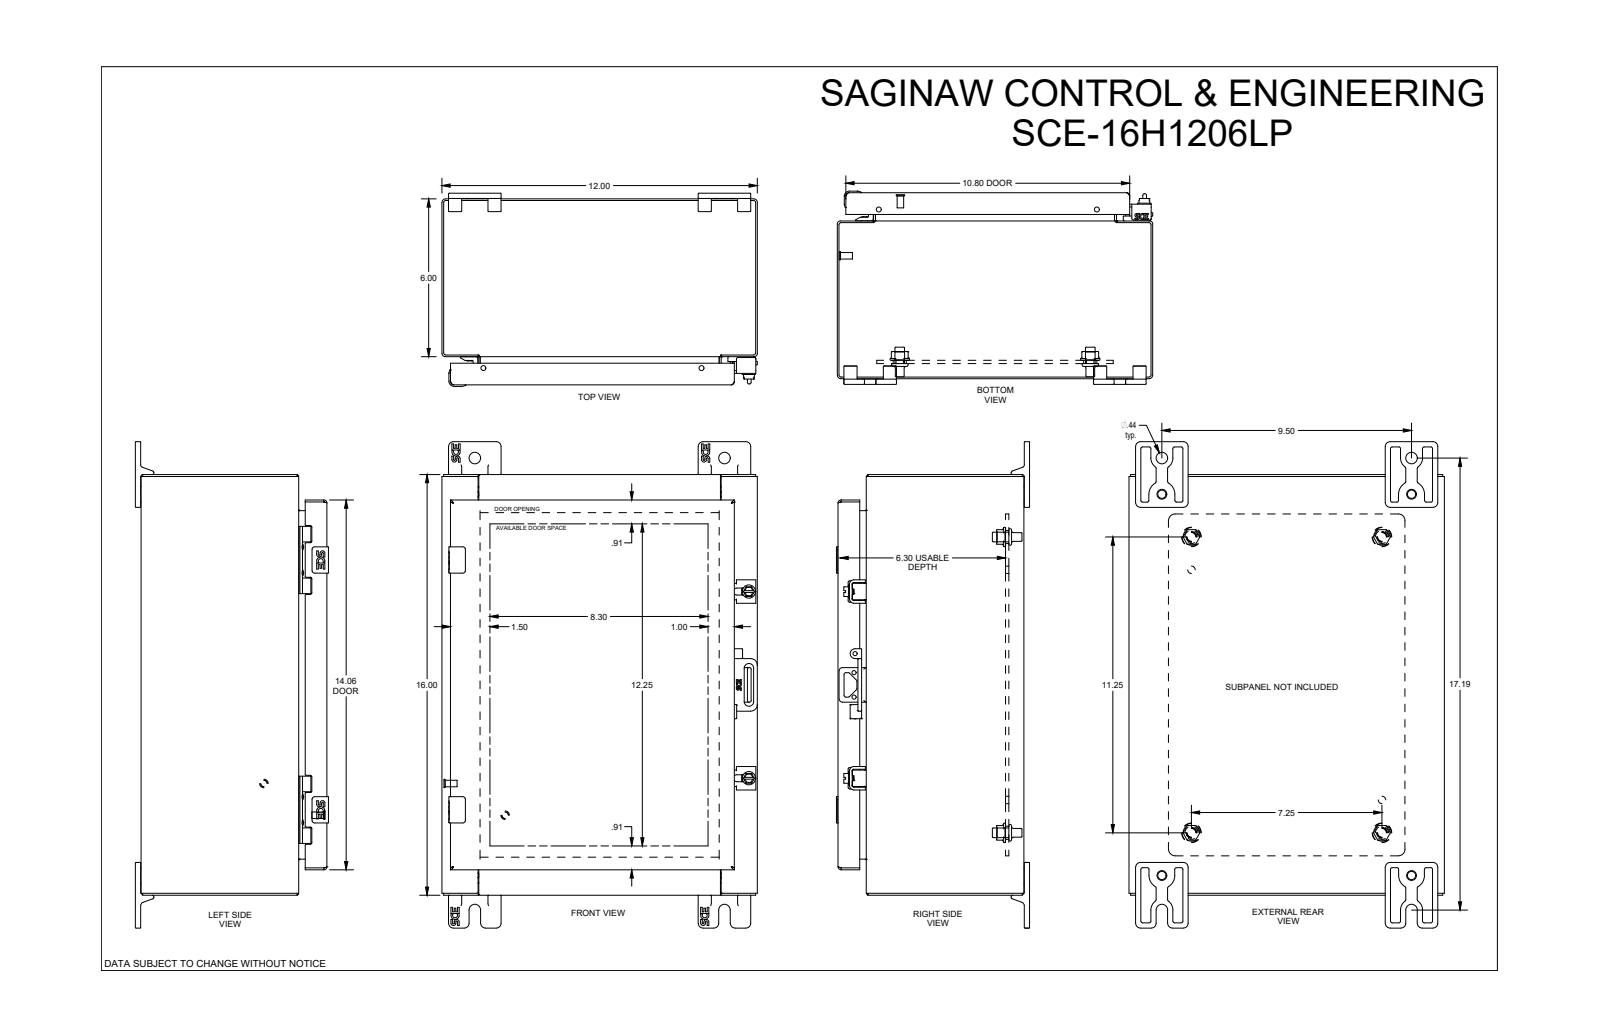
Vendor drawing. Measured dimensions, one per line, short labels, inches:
name: SCE-16H1206LP
written by: SolidWorks 2019 (AUTOMOTIVE_DESIGN)
unit: in
bodies: 56 solids, 3494 faces (1311 planar, 1010 cylindrical, 1173 other)
size: 18.5 × 12 × 7.288
volume: 87.85 in³; area: 2 096 in²
holes: 4× ⌀0.172, 4× ⌀0.205, 4× ⌀0.244, 4× ⌀0.266, 4× ⌀0.31, 4× ⌀0.312, 4× ⌀0.367, 4× ⌀0.375, 4× ⌀0.437, 4× ⌀0.5, 3× ⌀0.25, 2× ⌀0.04
bosses: 7× ⌀0.17, 6× ⌀0.25, 5× ⌀0.248, 4× ⌀0.59, 4× ⌀0.376, 4× ⌀0.366, 4× ⌀0.332, 4× ⌀0.24
rounds: 121× R0.025, 114× R0.01, 56× R0.015, 33× R0.063, 32× R0.03, 32× R0.06, 30× R0.062, 21× R0.185
face distances: 0.075, 0.06, 11.925, 6.938, 6.863, 0.075, 6.998, 6.922, 15.925, 5.925
hole spacings: 9.5, 1.976, 8.531, 12.924, 15.359, 11.51, 0.418, 0.493
